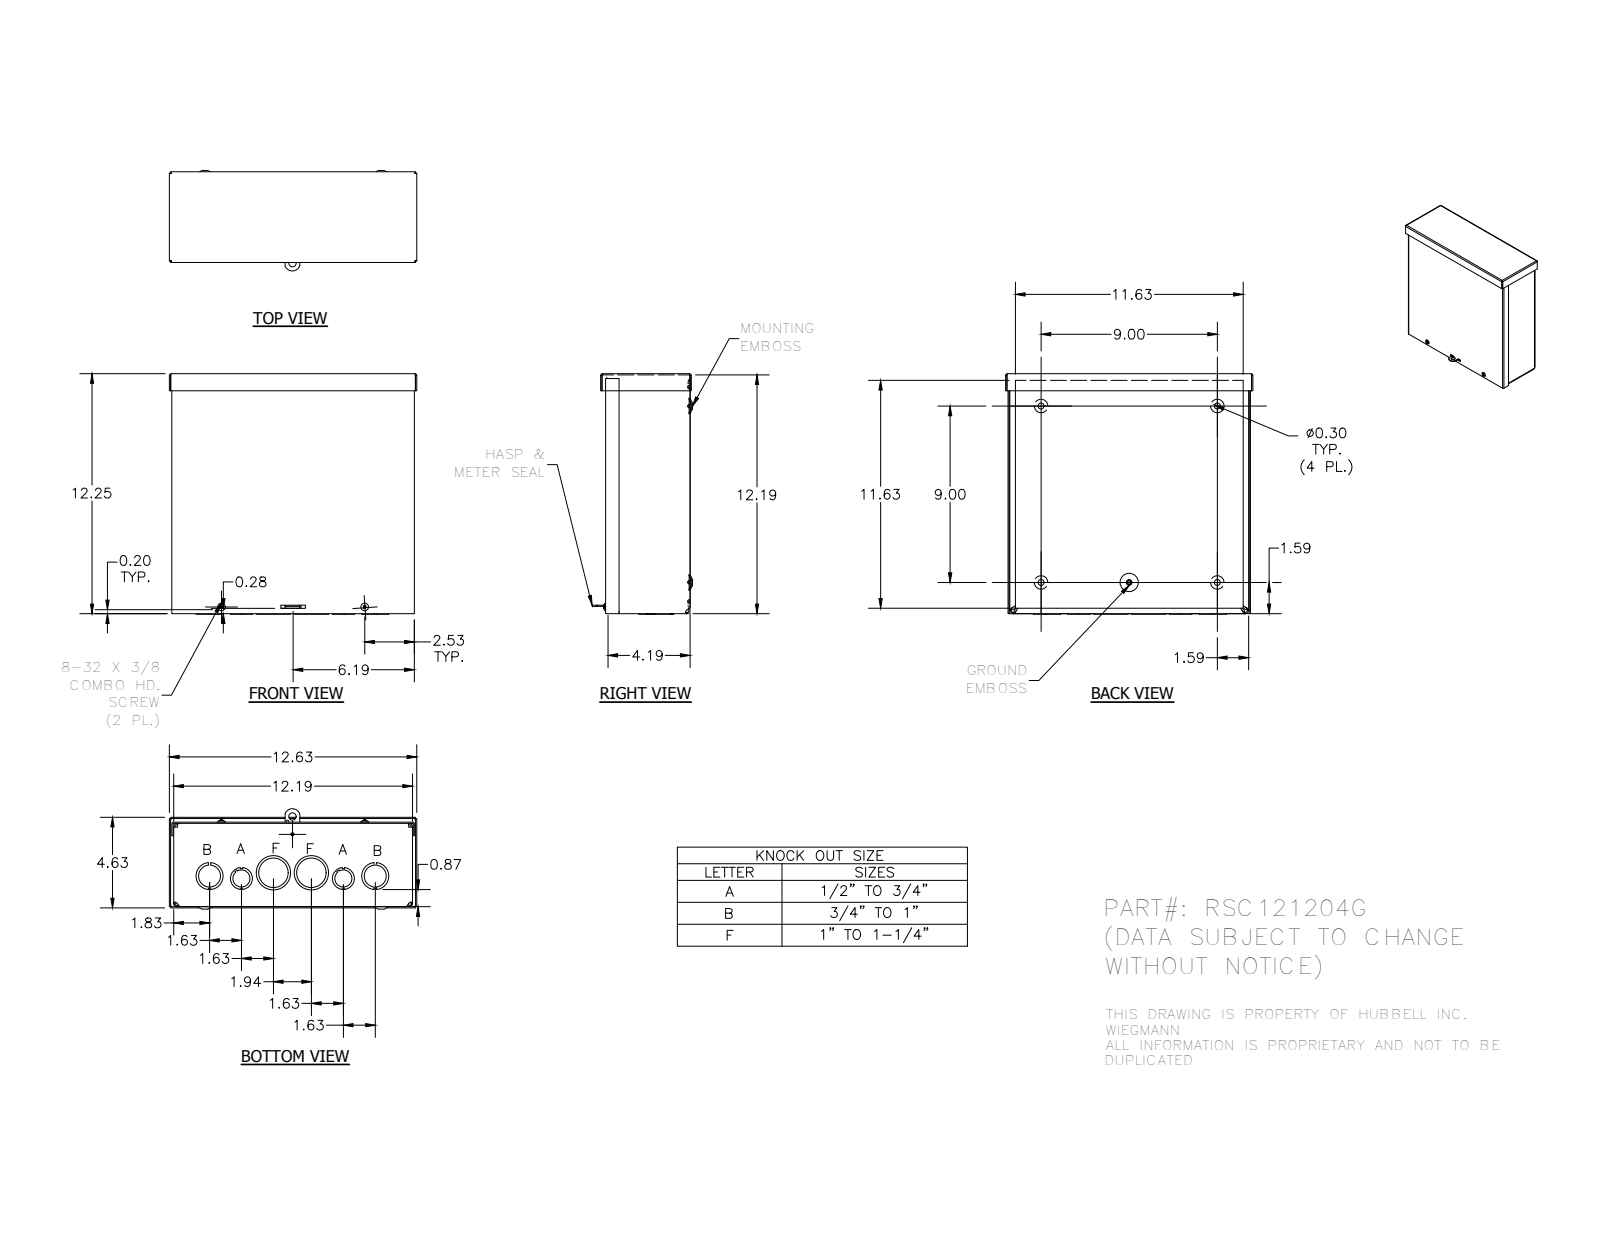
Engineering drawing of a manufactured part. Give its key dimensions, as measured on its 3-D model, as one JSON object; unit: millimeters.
{"part_name": "RSC121204G_WRAP; RSC1212G_LID; RSC1204G_CAP; 3183 (+4 more)", "step_written_by": "Autodesk Inventor 2014 (AUTOMOTIVE_DESIGN)", "units": "millimeters", "bodies": {"solids": 7, "faces": 551, "planar": 264, "cylindrical": 143, "other": 144}, "overall_size": [320.68, 311.93, 130.17], "volume_mm3": 664483, "surface_area_mm2": 855859, "round_holes": [[7.62, 4], [7.95, 4], [28.57, 4], [3.17, 2], [3.76, 2], [22.22, 2], [34.92, 2], [38.1, 2], [44.45, 2], [3.96, 1], [4.19, 1], [9.52, 1]], "round_bosses_or_shafts": [[9.75, 2], [4.17, 2], [5.8, 1]], "partial_cylinders_radius": [[0.25, 14], [0.79, 8], [2.37, 8], [3.17, 8], [4.75, 8], [0.79, 6], [0.63, 5], [1.4, 4]], "face_to_face_distances": [1.58, 307.99, 107.93, 106.35, 1.57, 1.59, 109.52, 107.94, 309.57, 3.15], "hole_center_spacings": [228.6, 34.43, 41.52, 42.07, 77, 82.91, 90.99, 114.3]}
